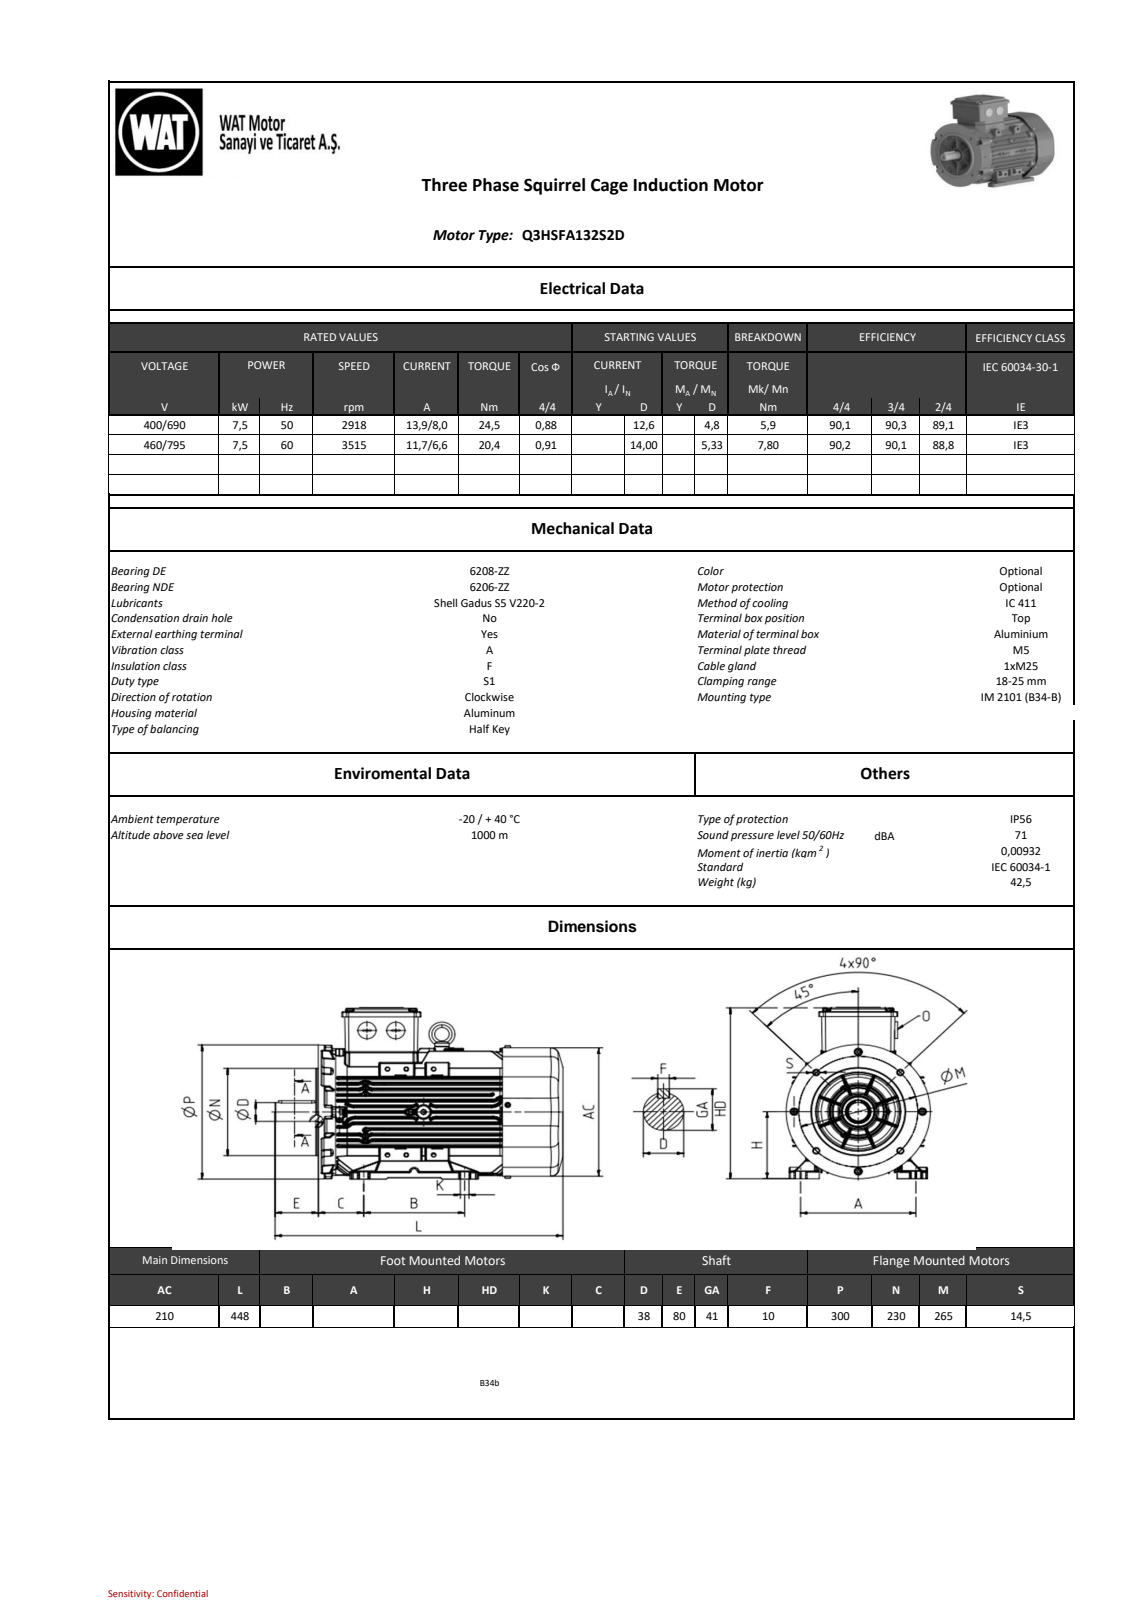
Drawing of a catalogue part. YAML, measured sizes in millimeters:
part_name: "QHS series_ 132_B5 _DEEP COVER__stp_objects"
step_written_by: "SIEMENS PLM Software NX2206.8101 (AP203_CONFIGURATION_CONTROLLED_3D_DESIGN_OF_MECHANICAL_PARTS_AND_ASSEMBLIES_MIM_LF)"
units: millimeters
bodies: {solids: 0, faces: 6871, planar: 1496, cylindrical: 2657, other: 2718}
overall_size: [447.4, 300.25, 300.25]
round_holes:
  - {diameter: 3.5, count: 4}
  - {diameter: 8, count: 1}
  - {diameter: 10.3, count: 1}
  - {diameter: 13, count: 1}
  - {diameter: 47, count: 1}
  - {diameter: 58.67, count: 1}
  - {diameter: 68, count: 1}
round_bosses_or_shafts:
  - {diameter: 6, count: 2}
  - {diameter: 230, count: 1}
  - {diameter: 188, count: 1}
  - {diameter: 46.5, count: 1}
  - {diameter: 40, count: 1}
  - {diameter: 38, count: 1}
  - {diameter: 37.4, count: 1}
  - {diameter: 30, count: 1}
partial_cylinders:
  - {radius: 2, count: 583}
  - {radius: 1, count: 571}
  - {radius: 0.8, count: 481}
  - {radius: 0.5, count: 299}
  - {radius: 3, count: 92}
  - {radius: 2.5, count: 8}
  - {radius: 5, count: 6}
  - {radius: 0.5, count: 4}
face_to_face_distances: [1, 10.99, 21.5, 35.96, 99.54, 90.43, 24.97, 68.93, 30.61, 4]
hole_center_spacings: [22.01]
